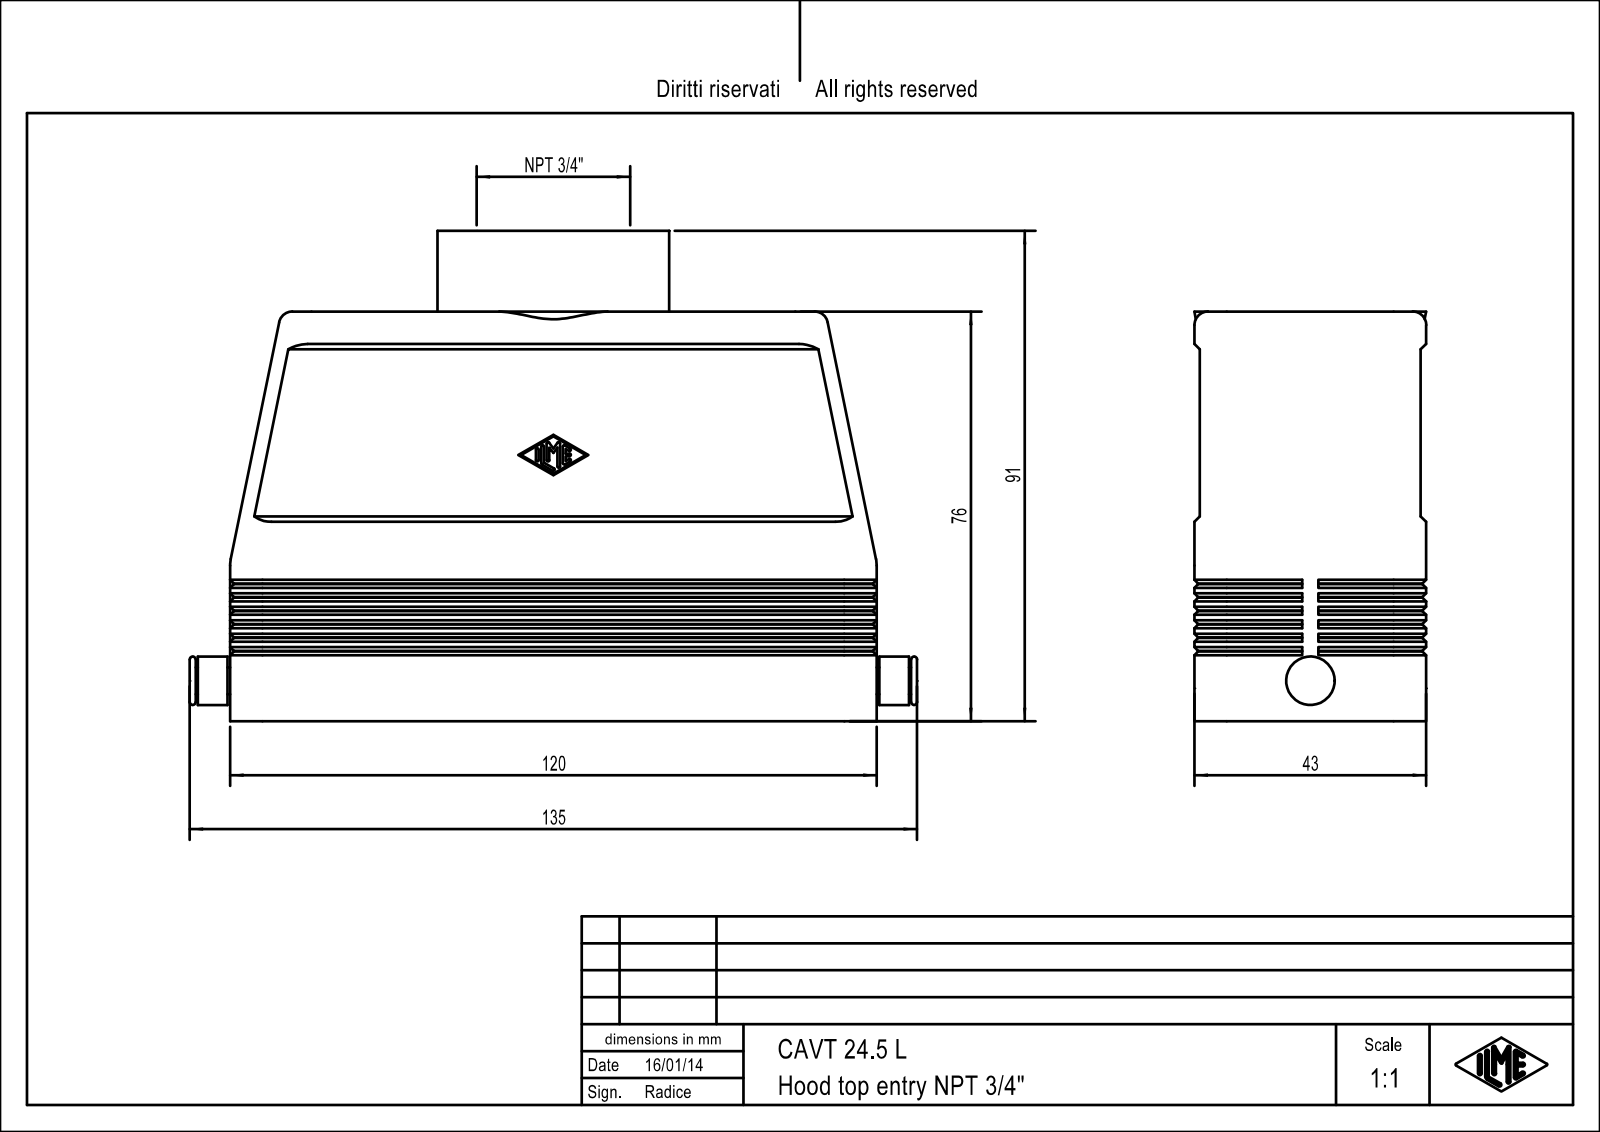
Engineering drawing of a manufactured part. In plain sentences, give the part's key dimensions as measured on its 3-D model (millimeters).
The part is named "CAVT_24.5_L". Its 3-D file was written by "Creo Elements/Direct Modeling 18.0B 02-Dec-2011 (C) Parametric Technology GmbH (AUTOMOTIVE_DESIGN)". It is 1 solid with 416 faces: 230 planar, 114 cylindrical and 72 other. Overall it measures 135 by 91 by 43 millimeters. Its volume is 98 912 cubic millimeters and its surface area 57 685 square millimeters. Round holes: 4 of diameter 4, 3 of diameter 2.46, 1 of diameter 2.46. Round bosses or shafts: 1 of diameter 43, 1 of diameter 9, 1 of diameter 5. Partial cylindrical surfaces (rounded edges, fillets, slot ends): 14 of radius 0.25, 10 of radius 6, 4 of radius 2, 4 of radius 2.5, 4 of radius 3, 4 of radius 5.3. The main face-to-face distances are 3, 37, 40, 2, 1, 42, 39, 43, 41, 9. The hole center spacings are 27, 104, 107.45.
